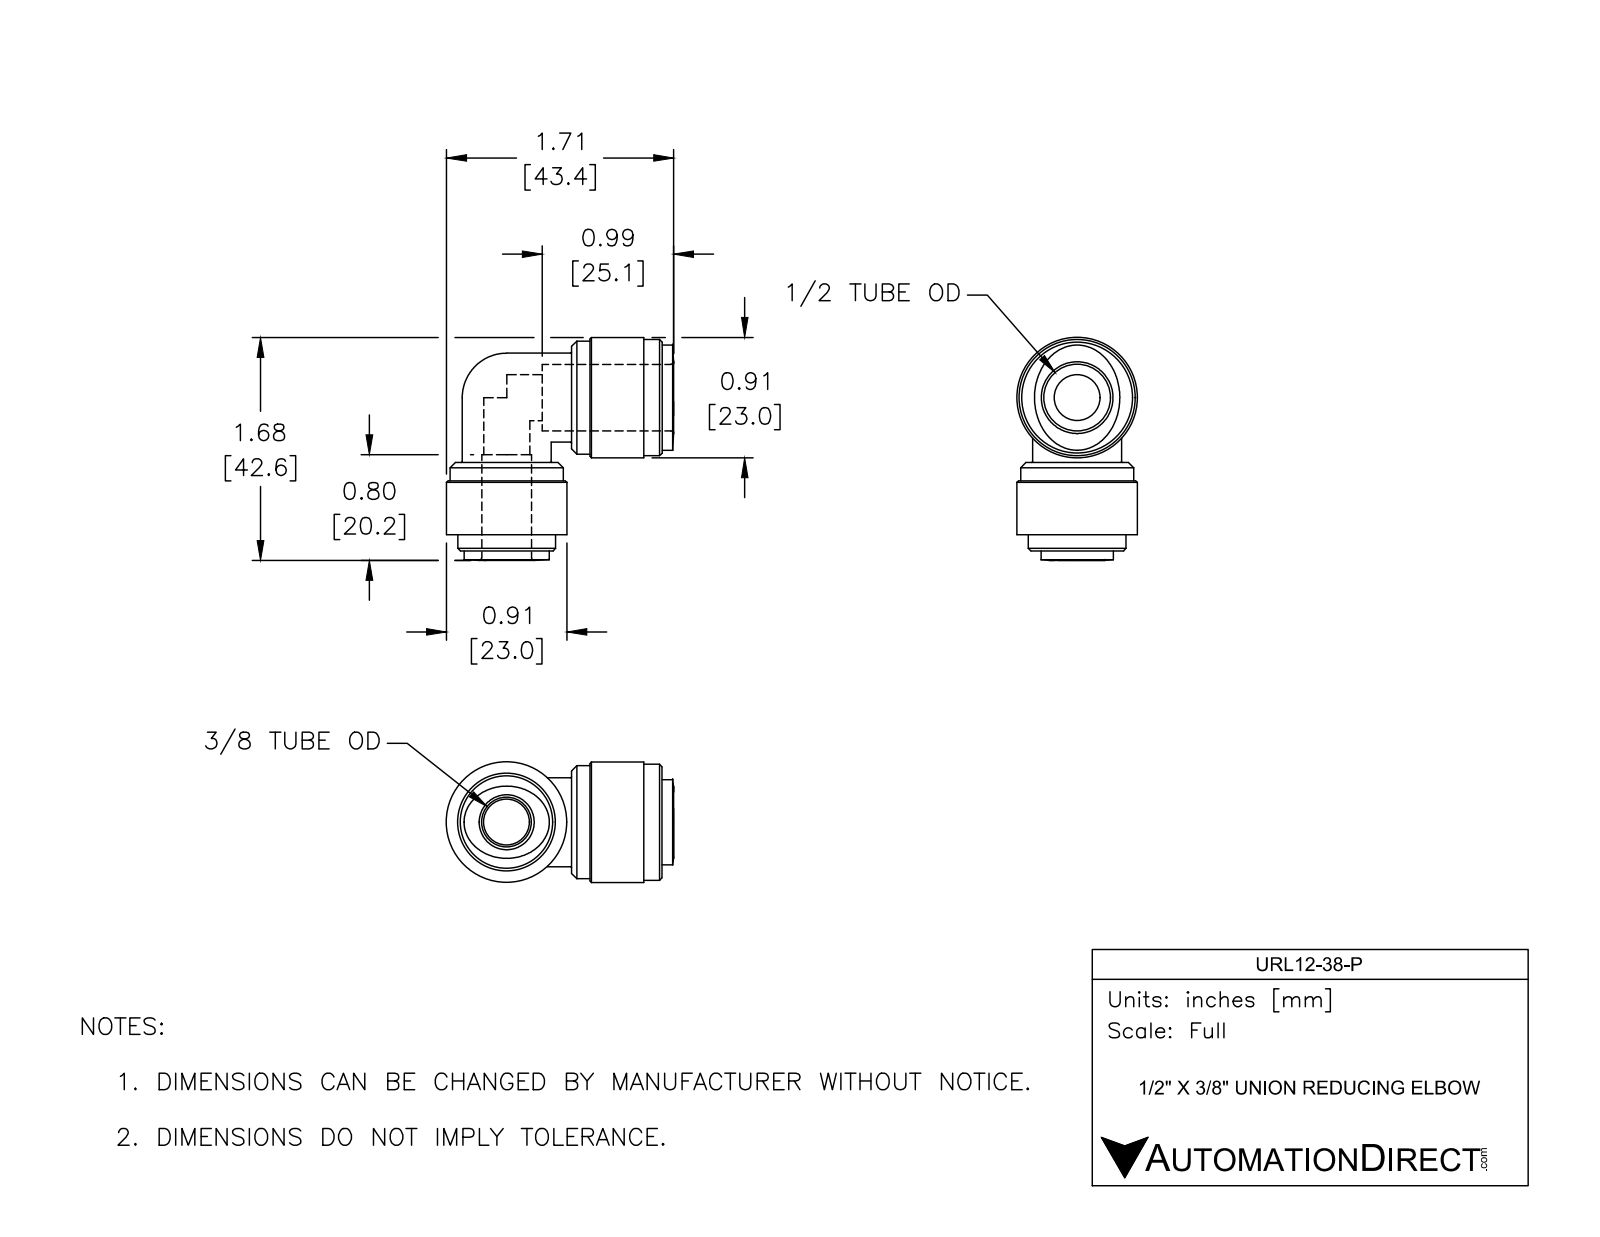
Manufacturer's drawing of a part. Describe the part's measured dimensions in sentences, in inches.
The part is named "URL12-38-P". Its 3-D file was written by "SolidWorks 2017 (AUTOMOTIVE_DESIGN)". It is 1 solid with 64 faces: 10 planar, 24 cylindrical and 30 other. Overall it measures 1.709 by 1.677 by 0.906 inches. Its volume is 0.847 cubic inches and its surface area 10.6 square inches. Round holes: 2 of diameter 0.346, 1 of diameter 0.374, 1 of diameter 0.5. Round bosses or shafts: 2 of diameter 0.906, 2 of diameter 0.85, 2 of diameter 0.669, 1 of diameter 0.874, 1 of diameter 0.736. The main face-to-face distances are 0.543, 0.138, 0.122, 0.902, 0.665, 0.22, 0.681, 0.406, 0.764, 0.528.
